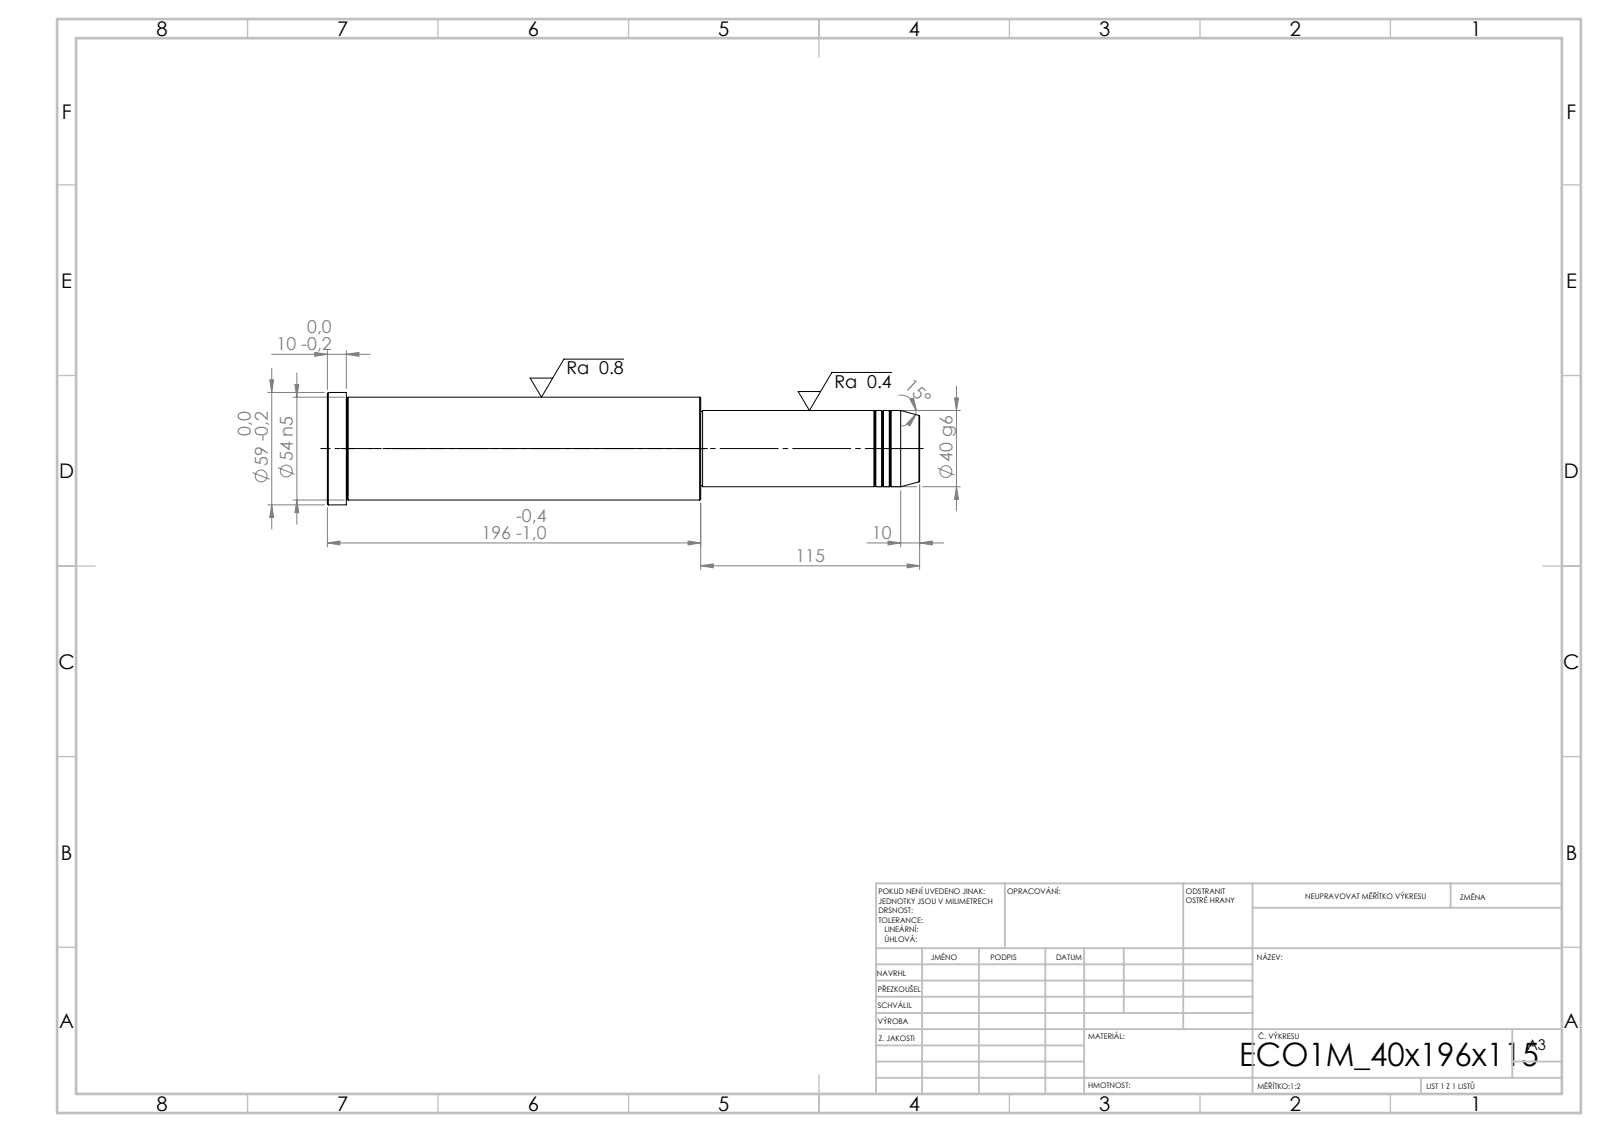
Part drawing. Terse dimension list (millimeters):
written by: SolidWorks 2019 (CONFIG_CONTROL_DESIGN)
unit: mm
bodies: 1 solid, 43 faces (5 planar, 14 cylindrical, 24 other)
size: 311 × 59 × 59
volume: 595 904 mm³; area: 53 273 mm²
bosses: 1× ⌀59, 1× ⌀54, 1× ⌀40, 1× ⌀39
face distances: 196, 115, 311, 301, 186, 10, 114, 1, 187, 197
